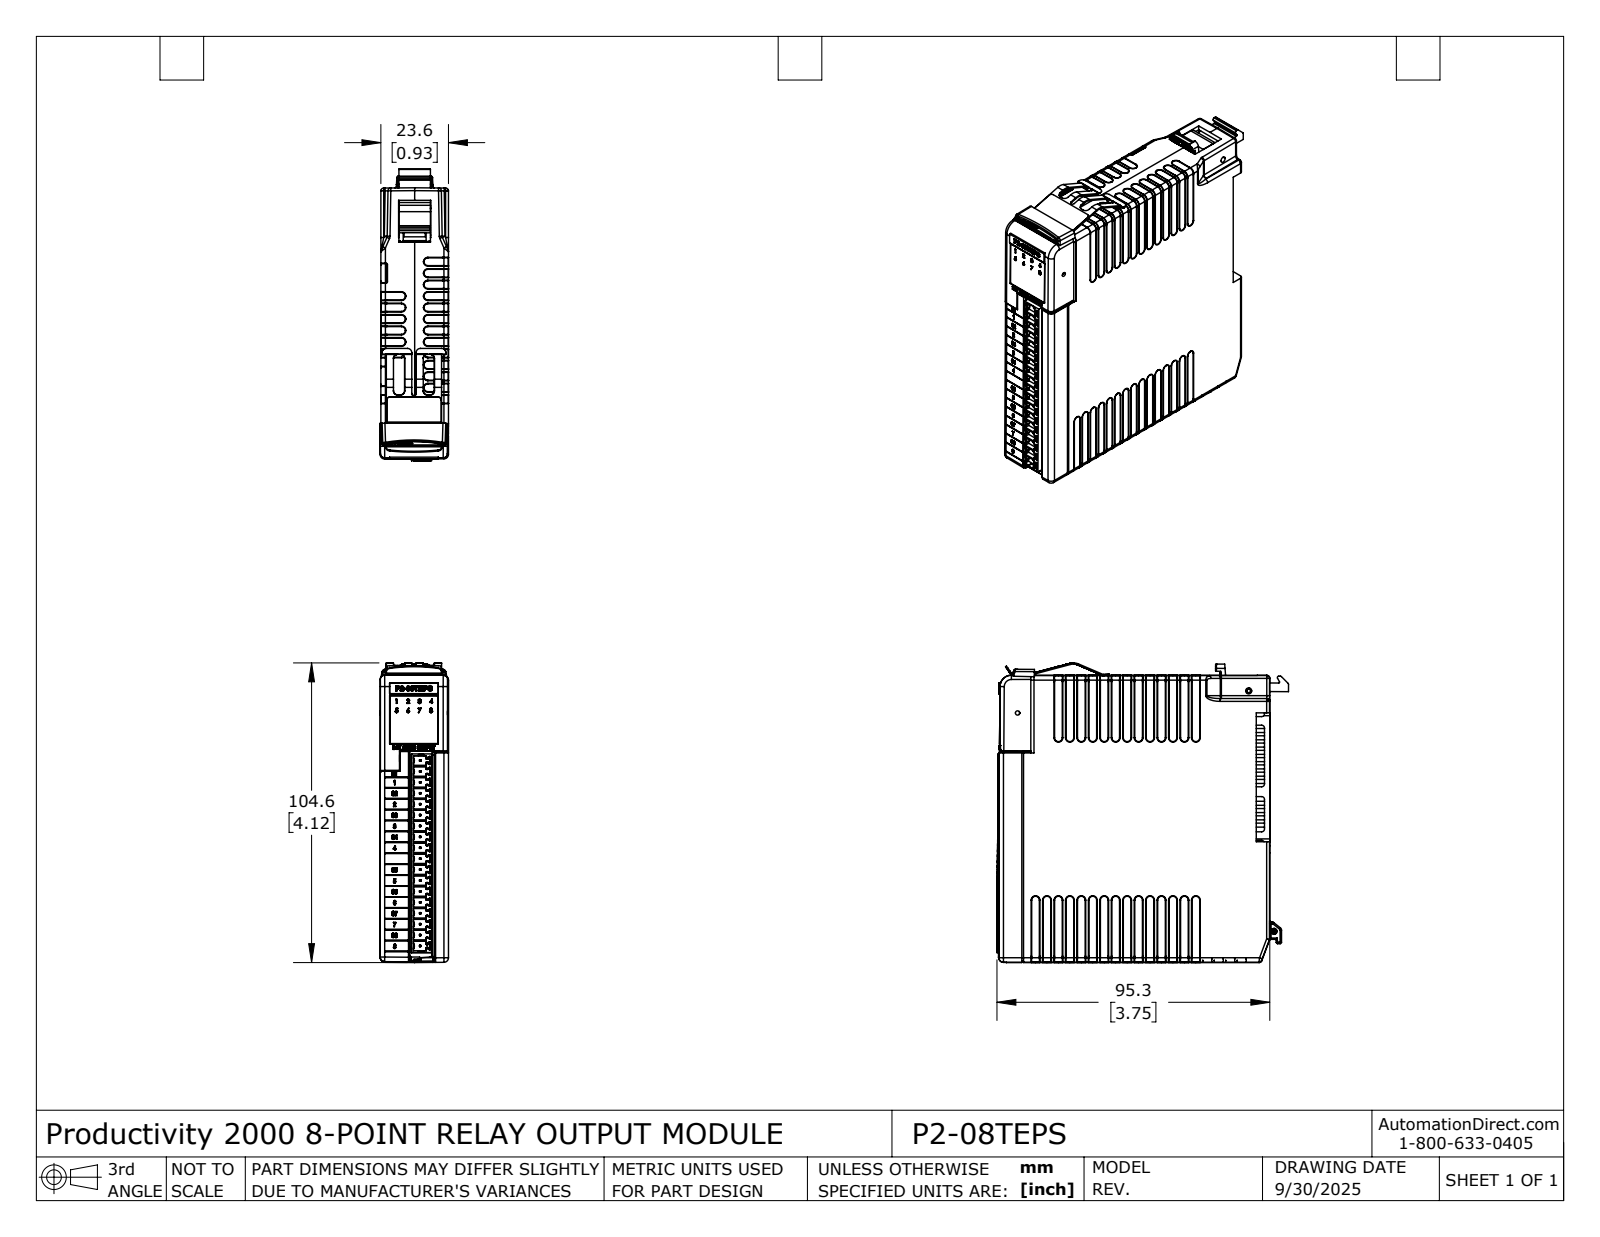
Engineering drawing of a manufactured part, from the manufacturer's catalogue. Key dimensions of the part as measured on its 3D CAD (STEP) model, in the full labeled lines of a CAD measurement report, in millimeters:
Part name (STEP PRODUCT): P2-08TEPS
STEP written by: SolidWorks 2024 (AUTOMOTIVE_DESIGN)
Units: millimetres
Bodies: 9 solids, 3967 faces (2058 planar, 833 cylindrical, 1076 other)
Overall size (bounding box): 104.6 × 101.8 × 23.9
Volume: 204 200 mm³ · Surface area: 45 570 mm²
Round holes (diameter × count): ⌀1.6 ×13, ⌀1.2 ×3, ⌀1.5 ×1, ⌀2 ×1, ⌀2.1 ×1, ⌀2.5 ×1
Partial cylindrical surfaces — rounded edges, fillets, slot ends (radius × count): R0.5 ×350, R0.2 ×76, R1 ×74, R1.5 ×22, R1.6 ×18, R1.6 ×13, R2 ×6, R0.3 ×5
Main face-to-face distances: 23.6, 23.6, 23.5, 23.6, 100.3, 1.6, 22, 4, 16.4, 100.2
Hole centre spacings: 5.1, 10.2, 15.2, 20.3, 25.4, 30.5, 35.6, 40.6
